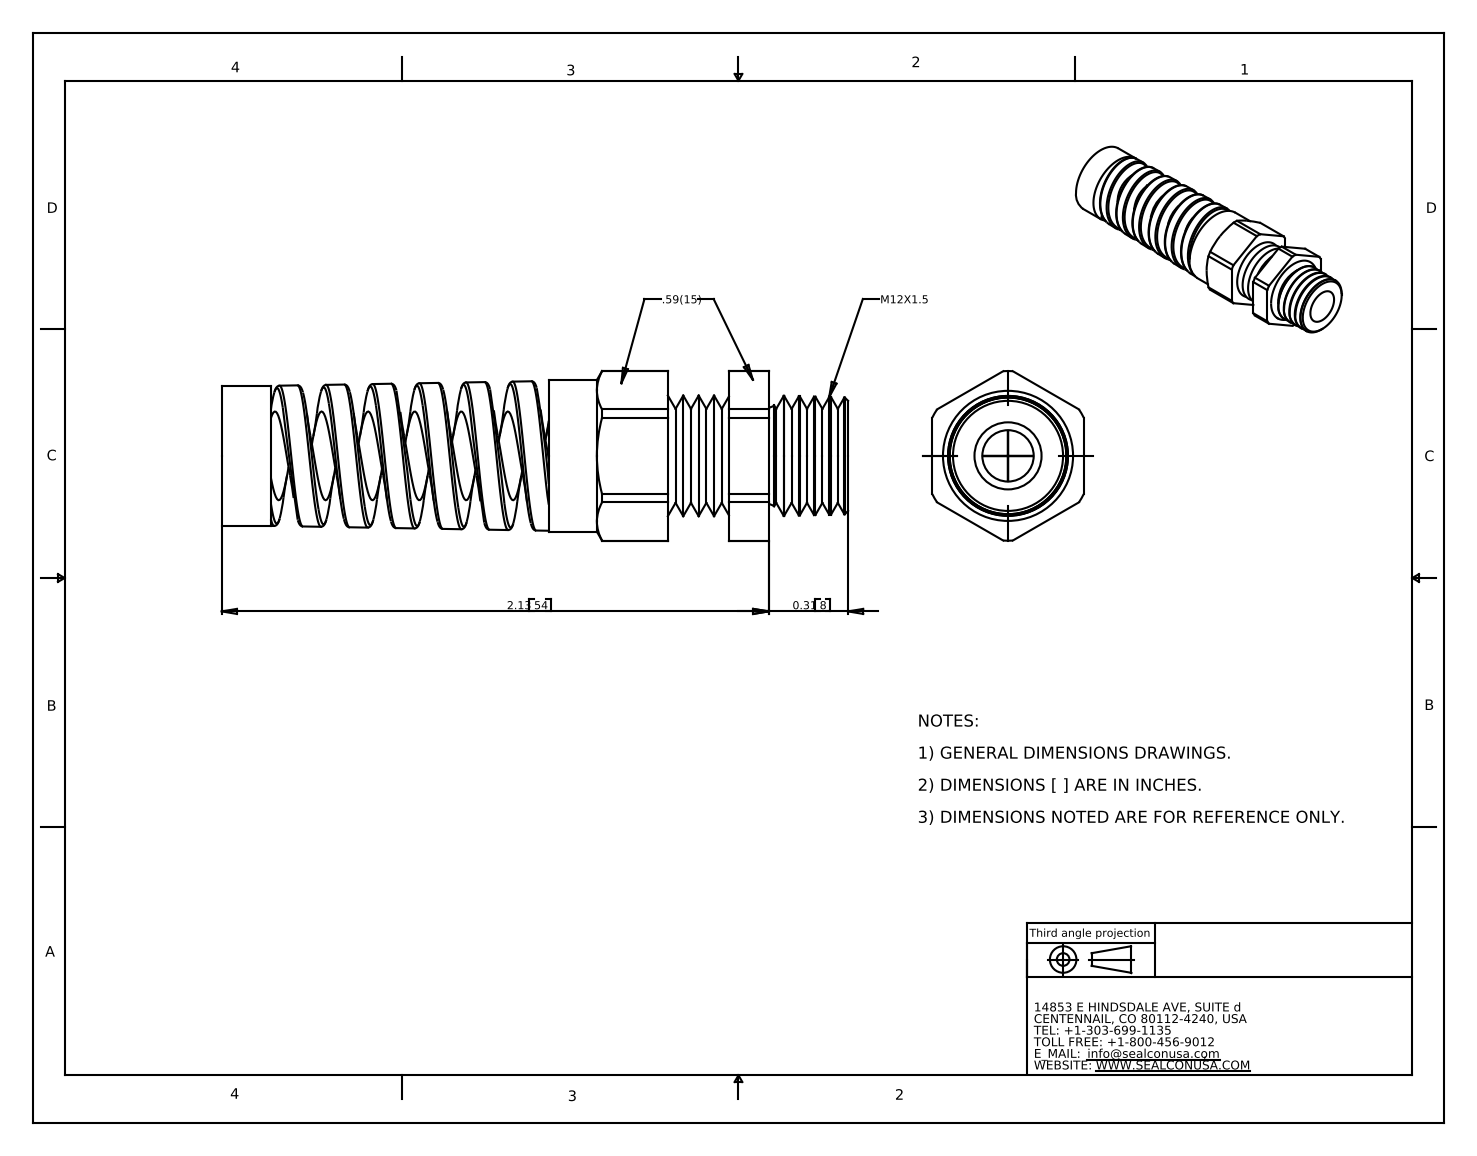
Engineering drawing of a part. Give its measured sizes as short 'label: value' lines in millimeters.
name: CF12MR-GY
written by: SolidWorks 2007 (CONFIG_CONTROL_DESIGN)
unit: mm
bodies: 1 solid, 131 faces (19 planar, 34 cylindrical, 78 other)
size: 62 × 16.8 × 15
volume: 5 370 mm³; area: 5 383 mm²
holes: 1× ⌀5.1, 1× ⌀8.8, 1× ⌀11.9
bosses: 1× ⌀15, 1× ⌀13.9
rounds: 1× R8.4
face distances: 15, 32.4, 50.2, 17.8, 44.1, 11.8, 6, 54.1, 21.7, 10
